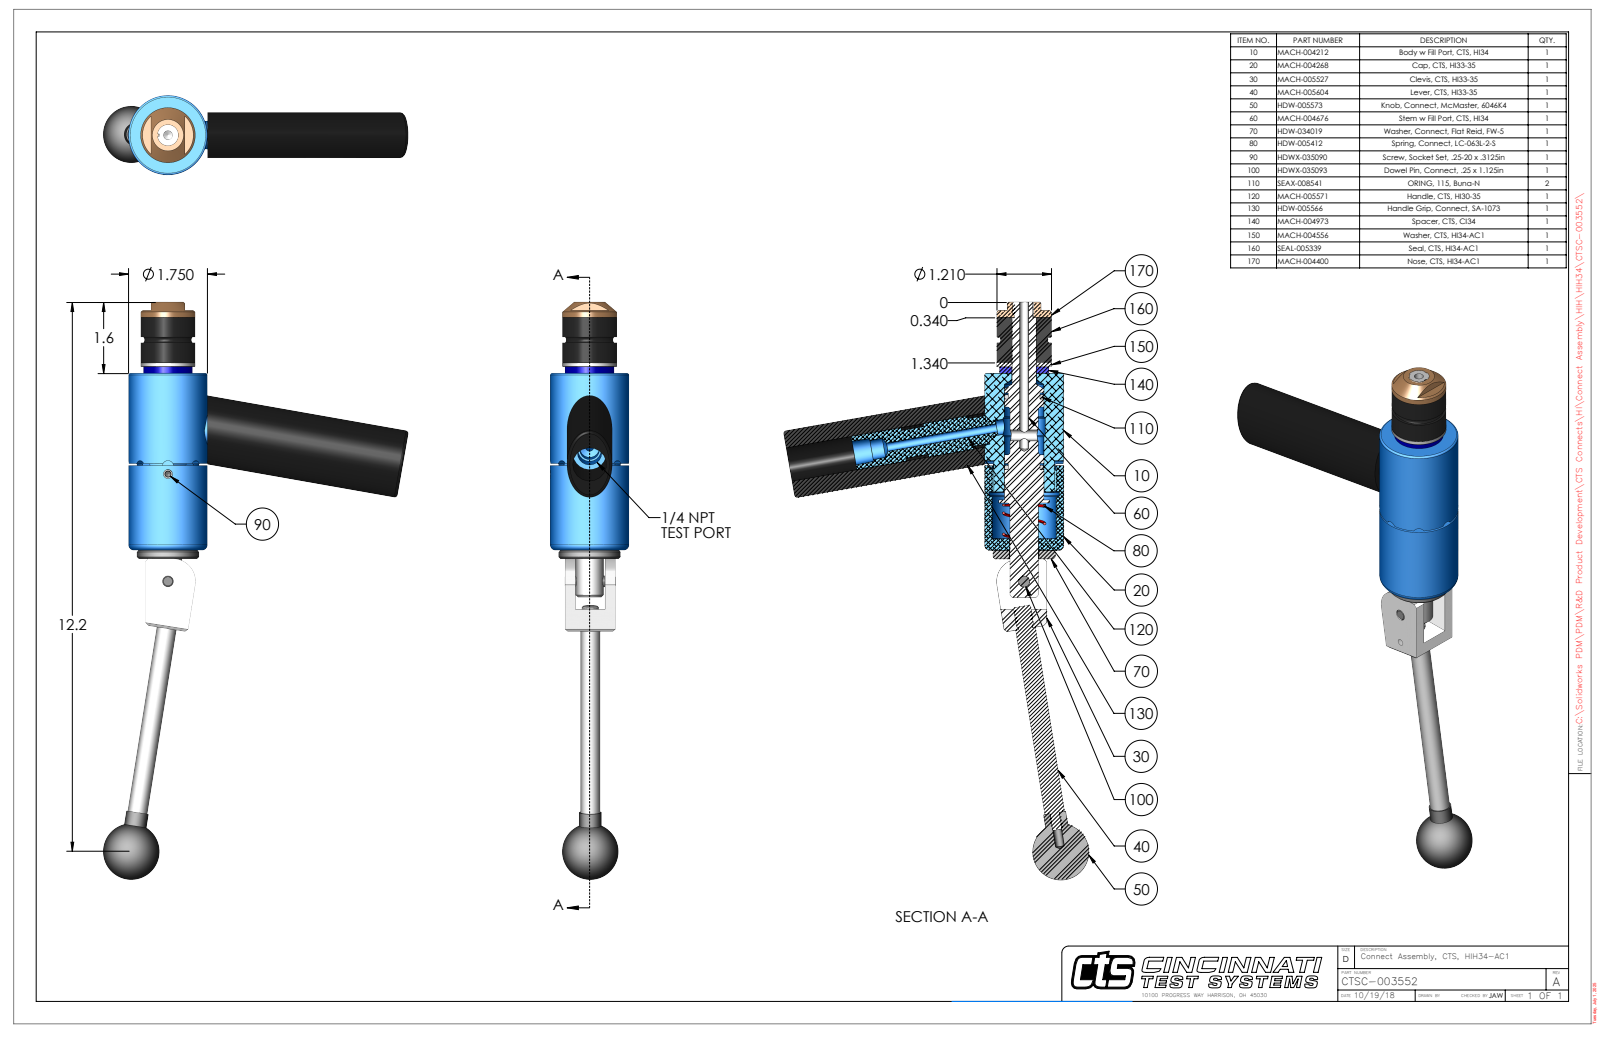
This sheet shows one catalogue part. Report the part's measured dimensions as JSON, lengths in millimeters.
{"part_name": "CTSC-003552", "step_written_by": "SolidWorks 2023 (AUTOMOTIVE_DESIGN)", "units": "millimeters", "bodies": {"solids": 11, "faces": 303, "planar": 109, "cylindrical": 125, "other": 69}, "overall_size": [325, 171.8, 44.5], "volume_mm3": 301500, "surface_area_mm2": 75680, "round_holes": [[5.1, 2], [3.8, 1], [4.7, 1], [5.2, 1], [6.3, 1], [6.4, 1], [6.4, 1], [8, 1], [10.7, 1], [11.1, 1], [13.5, 1], [13.7, 1]], "round_bosses_or_shafts": [[12.7, 2], [11.2, 2], [6.4, 2], [44.5, 1], [35.1, 1], [30.7, 1], [27.7, 1], [19.1, 1]], "partial_cylinders_radius": [[3.2, 4], [0.7, 2], [4.6, 1], [8.4, 1], [12.7, 1], [17.7, 1], [21, 1]], "face_to_face_distances": [99.6, 31.4, 131, 25.4, 6, 105.6, 27.8, 2.4, 3.6, 103.2], "hole_center_spacings": [18.8, 60.4, 79.1]}
